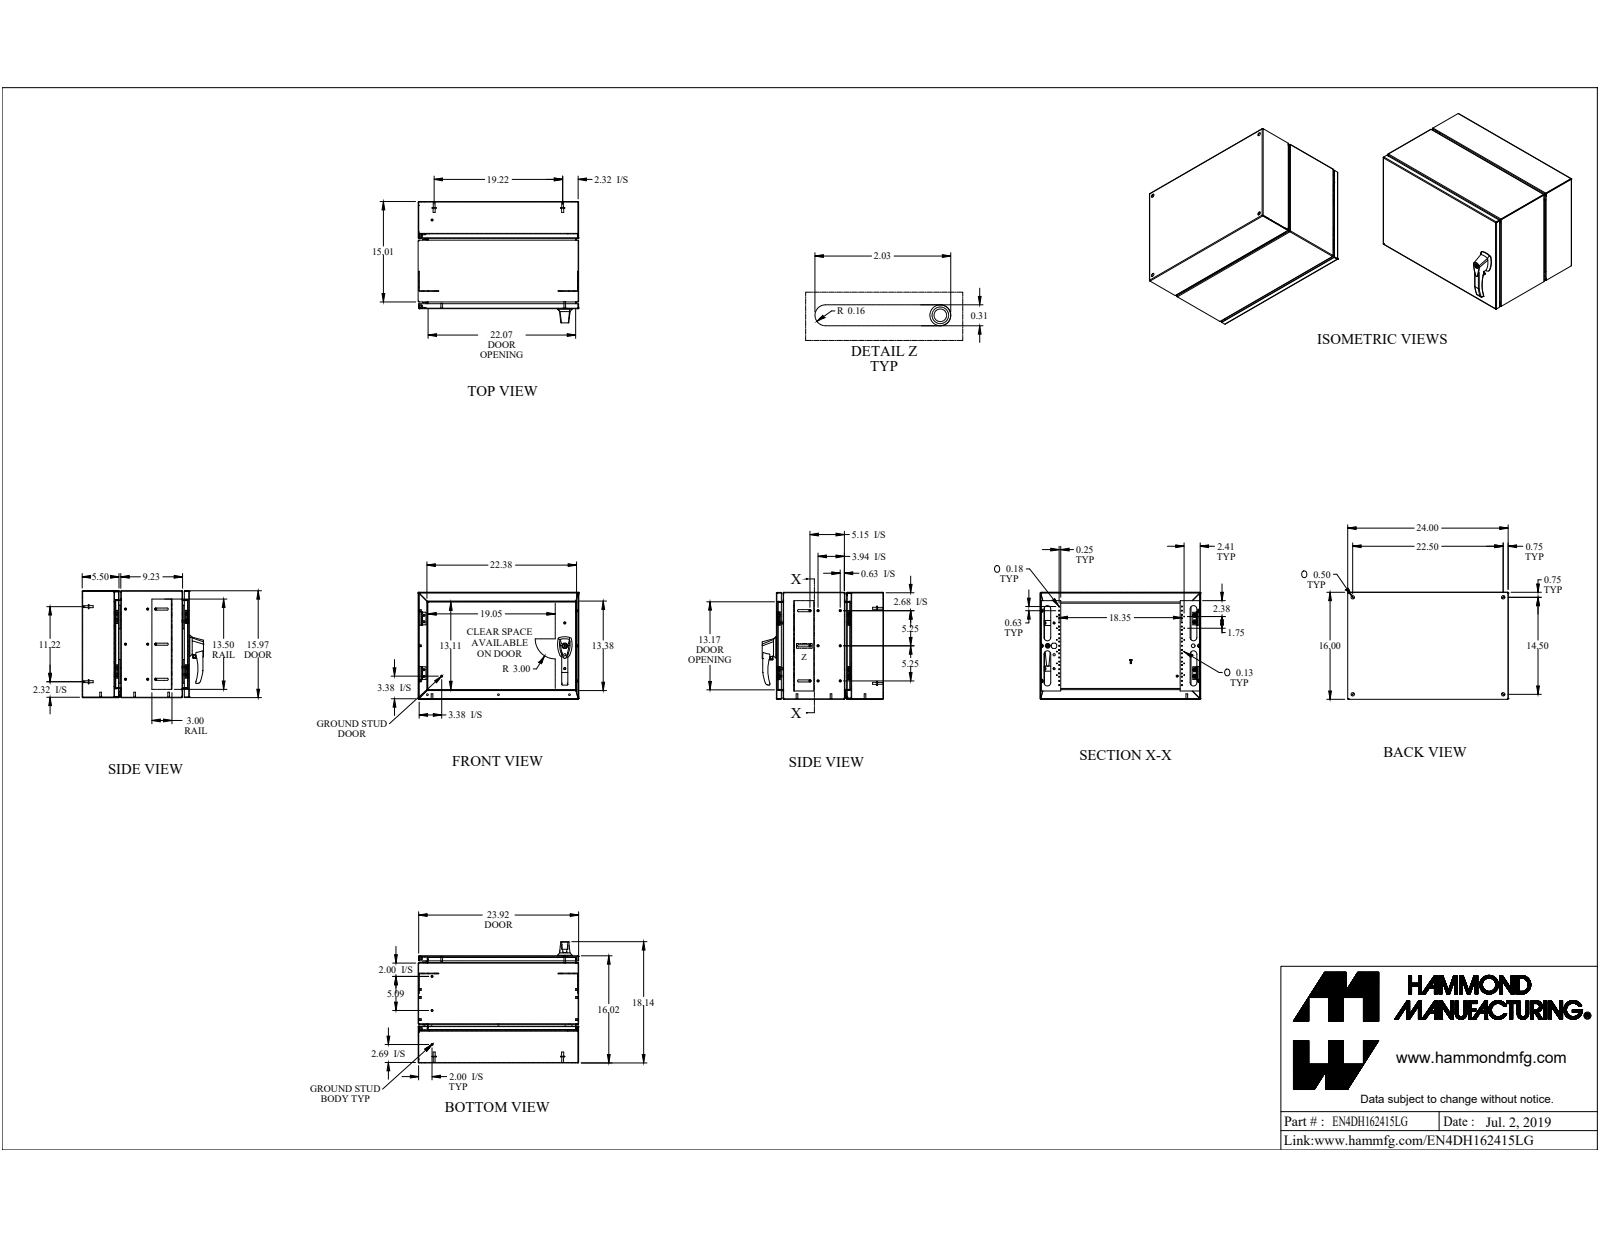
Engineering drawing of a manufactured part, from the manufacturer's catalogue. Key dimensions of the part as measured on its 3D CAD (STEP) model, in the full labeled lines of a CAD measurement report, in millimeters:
Part name (STEP PRODUCT): EN4DH162415LG
STEP written by: SolidWorks 2019 (CONFIG_CONTROL_DESIGN)
Units: millimetres
Bodies: 173 solids, 3616 faces (1986 planar, 911 cylindrical, 719 other)
Overall size (bounding box): 609.6 × 460.6 × 406.4
Volume: 3 933 000 mm³ · Surface area: 3 961 000 mm²
Round holes (diameter × count): ⌀4.5 ×42, ⌀6.4 ×17, ⌀5 ×15, ⌀3.2 ×12, ⌀4.8 ×8, ⌀4.9 ×8, ⌀6 ×8, ⌀6.5 ×7, ⌀7 ×7, ⌀6.7 ×5, ⌀7 ×4, ⌀12.7 ×4
Round bosses / shafts (diameter × count): ⌀6.4 ×21, ⌀8 ×13, ⌀6 ×10, ⌀12 ×8, ⌀11 ×8, ⌀4.7 ×8, ⌀15.9 ×7, ⌀15.9 ×6
Partial cylindrical surfaces — rounded edges, fillets, slot ends (radius × count): R0.9 ×38, R2.7 ×38, R0.5 ×34, R3.6 ×20, R6.4 ×18, R3.2 ×17, R1.5 ×16, R2 ×12
Main face-to-face distances: 1.8, 405.1, 1.8, 404.6, 607.8, 403.3, 406.9, 404.6, 406.4, 1.8
Hole centre spacings: 88.9, 49.1, 28.6, 28.6, 133.4, 176, 177.8, 25
